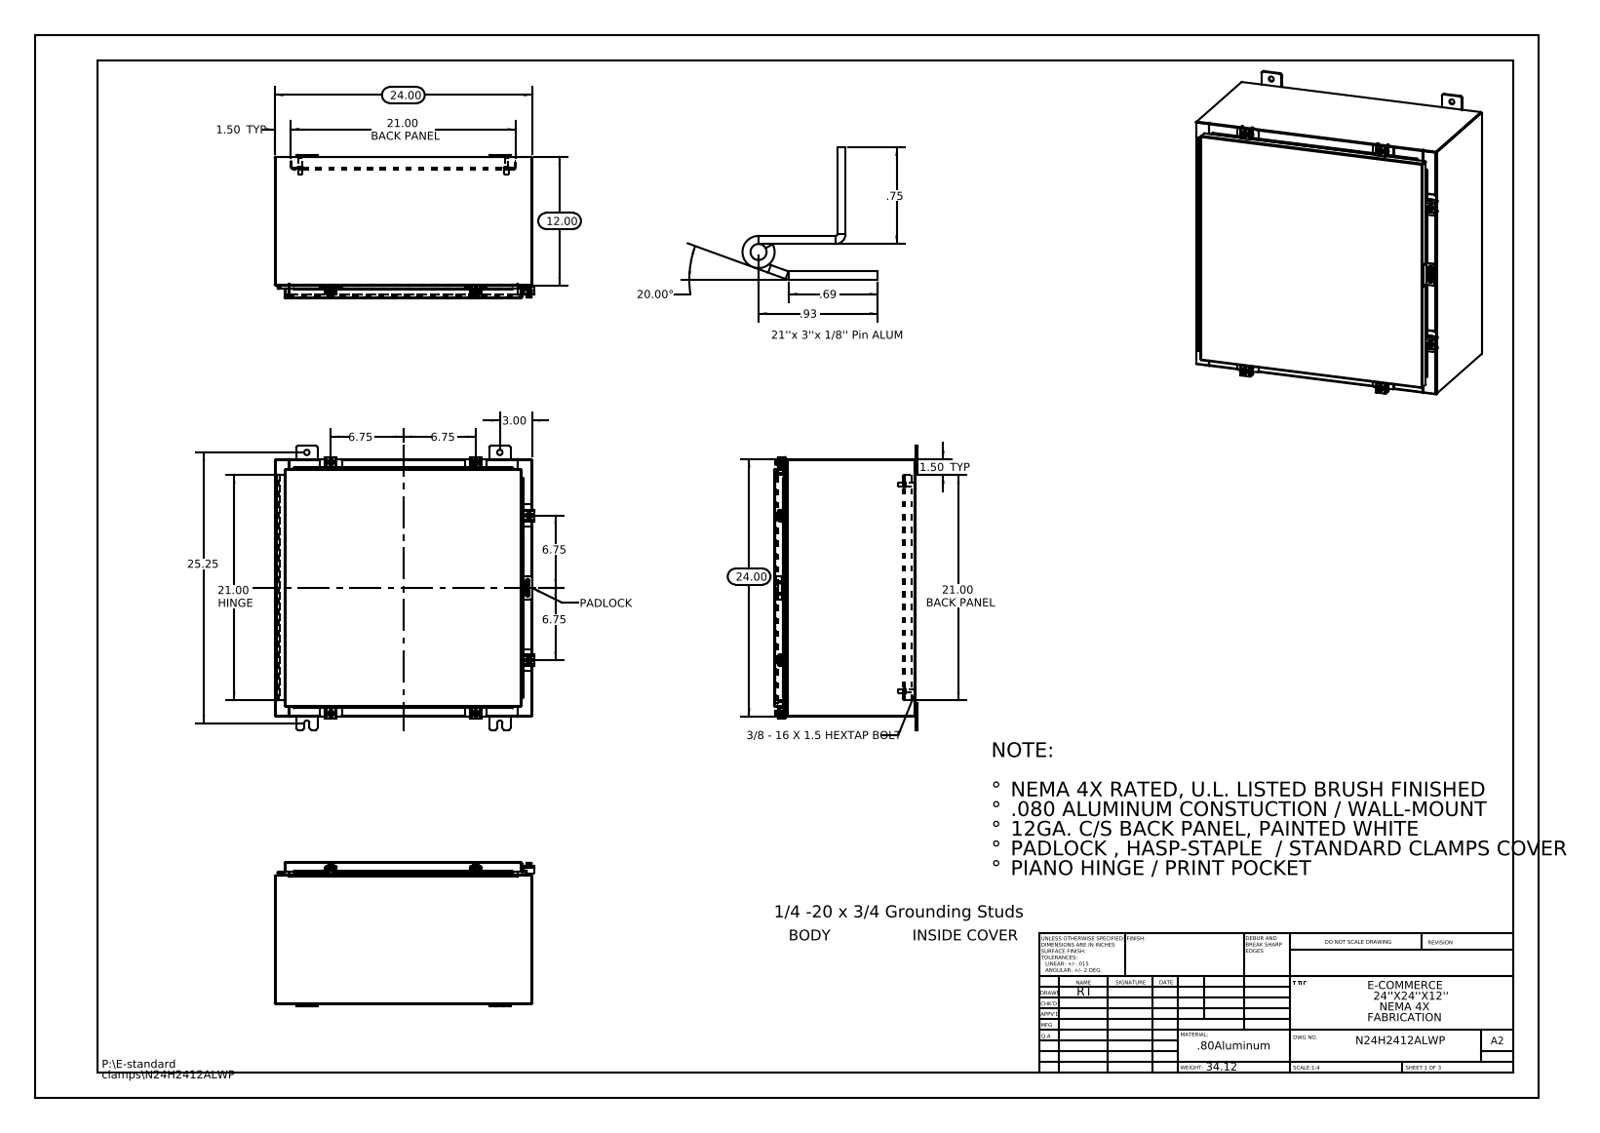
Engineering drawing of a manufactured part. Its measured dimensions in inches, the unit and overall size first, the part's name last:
Units: inches
Overall size (bounding box): 26.5 × 24.211 × 13.389
Round holes (diameter × count): ⌀0.5 ×8, ⌀0.213 ×6, ⌀0.26 ×6, ⌀0.125 ×2, ⌀0.125 ×1
Round bosses / shafts (diameter × count): ⌀0.25 ×7, ⌀0.5 ×6, ⌀0.399 ×6, ⌀0.625 ×4, ⌀0.375 ×4, ⌀0.33 ×4
Partial cylindrical surfaces — rounded edges, fillets, slot ends (radius × count): R0.06 ×30, R0.013 ×25, R0.19 ×24, R0.088 ×21, R0.12 ×12, R0.141 ×12, R0.125 ×10, R0.05 ×9
Main face-to-face distances: 0.075, 23.925, 13.126, 23.85, 24, 13.201, 13.051, 0.104, 1, 1.075
Hole centre spacings: 16.509, 19.134, 21.544, 26.907, 13.5, 1.858, 2.277, 2.423
Volume: 244.7 in³ · Surface area: 6 196 in²
Bodies: 47 solids, 1709 faces (908 planar, 705 cylindrical, 96 other)
Part name (STEP PRODUCT): N24H2412ALWP Bottom; N24H2412ALWP Hinge Cover Side; N24H2412ALWP; N24H2412ALWP 125 Pin Hinge (+8 more)
STEP written by: SolidWorks 2013 (CONFIG_CONTROL_DESIGN)
